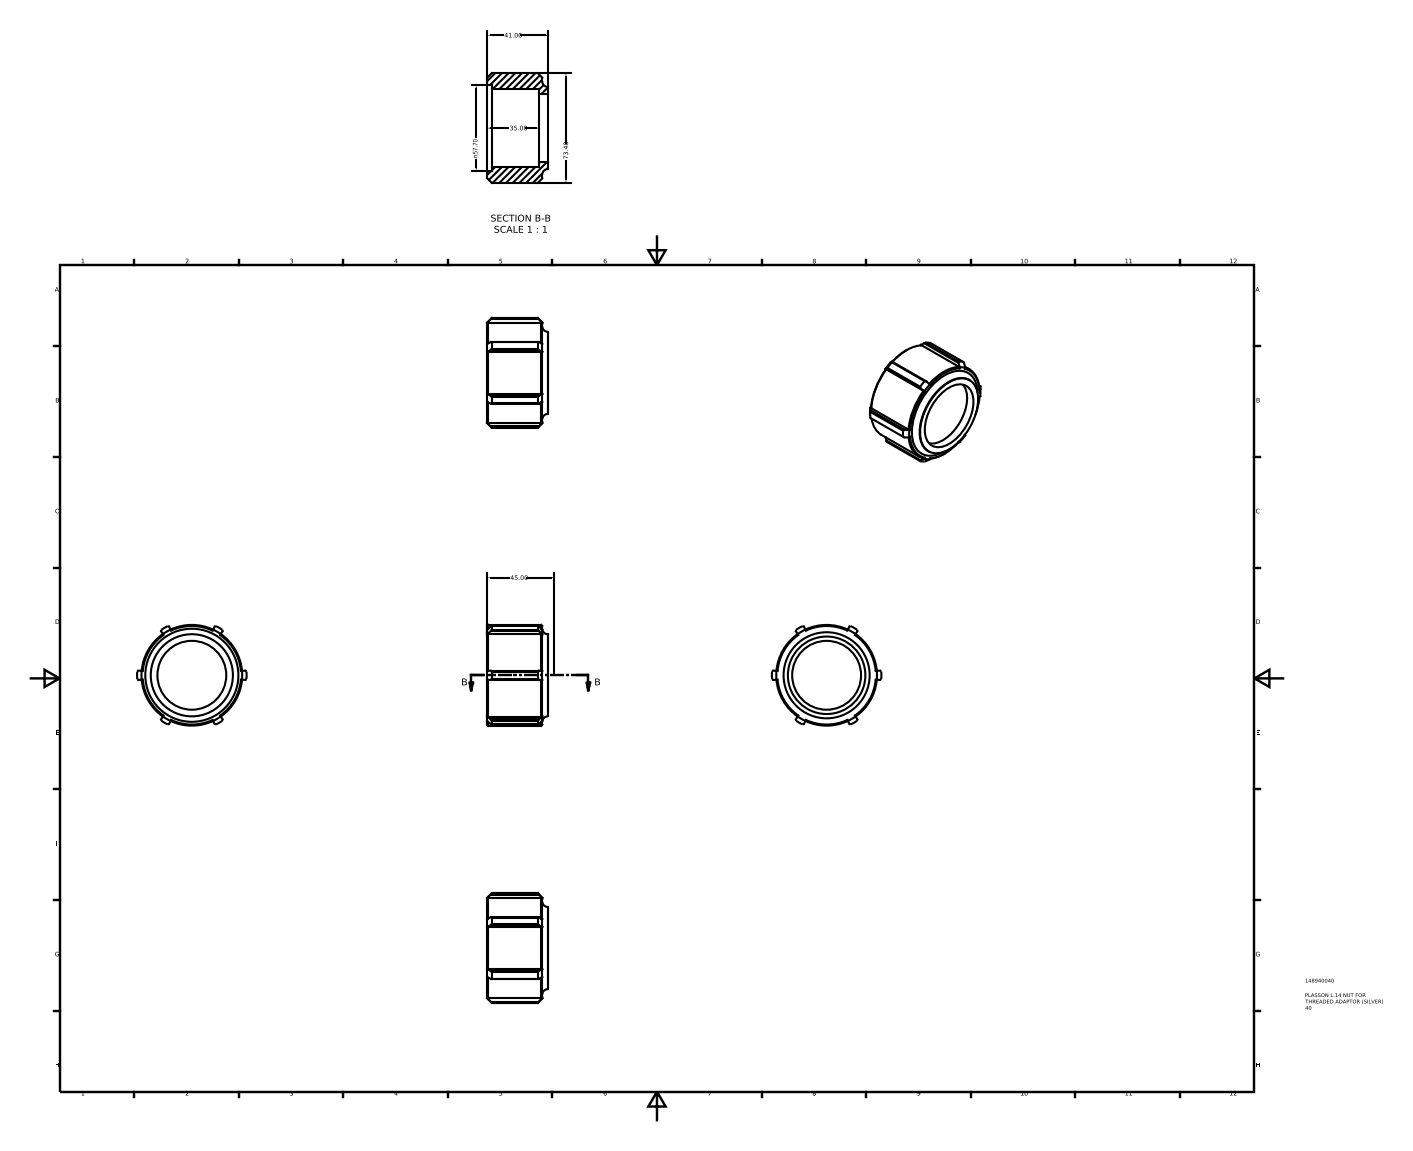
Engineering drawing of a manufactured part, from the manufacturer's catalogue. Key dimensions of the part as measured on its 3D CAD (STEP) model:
Part name (STEP PRODUCT): 148940040
STEP written by: Autodesk Inventor 2015 (AUTOMOTIVE_DESIGN)
Units: millimetres
Bodies: 1 solid, 70 faces (29 planar, 16 cylindrical, 25 other)
Overall size (bounding box): 73.4 × 67.53 × 41
Volume: 59 998 mm³ · Surface area: 19 806 mm²
Round holes (diameter × count): ⌀46.16 ×1, ⌀51.93 ×1, ⌀57.7 ×1
Round bosses / shafts (diameter × count): ⌀67.53 ×1, ⌀55.05 ×1
Partial cylindrical surfaces — rounded edges, fillets, slot ends (radius × count): R36.7 ×1
Main face-to-face distances: 41, 3.5, 37.5, 35, 31.5, 6, 36.9, 33.4, 1.9, 4.1
